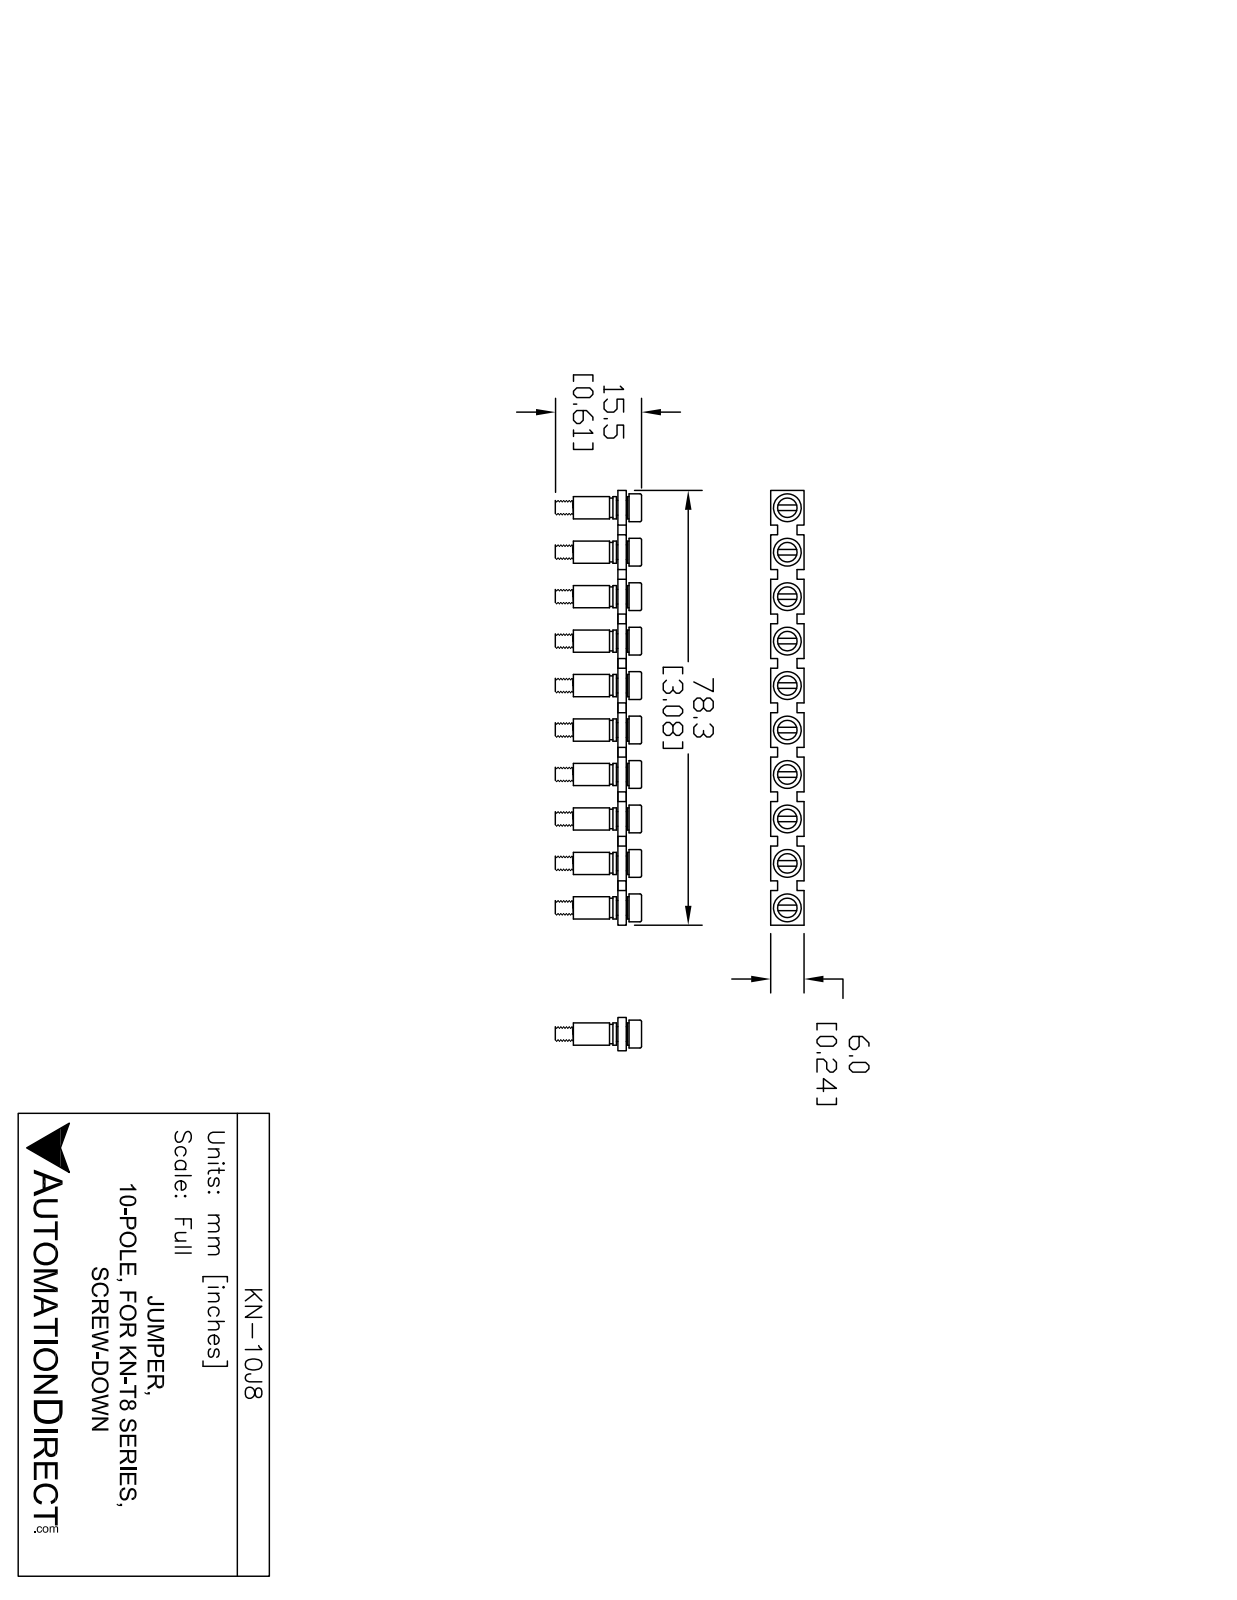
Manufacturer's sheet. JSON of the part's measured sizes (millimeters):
{"part_name": "KN-10J8", "step_written_by": "SolidWorks 2014 (AUTOMOTIVE_DESIGN)", "units": "millimeters", "bodies": {"solids": 31, "faces": 508, "planar": 238, "cylindrical": 210, "other": 60}, "overall_size": [78.25, 15.5, 6], "volume_mm3": 2042, "surface_area_mm2": 5574, "round_holes": [[2.8, 10], [3, 10], [3.15, 10], [3.5, 10]], "round_bosses_or_shafts": [[5, 10], [4, 10], [2.65, 10]], "face_to_face_distances": [1.5, 2, 1.75, 2.25, 0.5, 8, 1.25, 1, 2.75, 6], "hole_center_spacings": [8, 16, 24, 32, 40, 48, 56, 64]}
